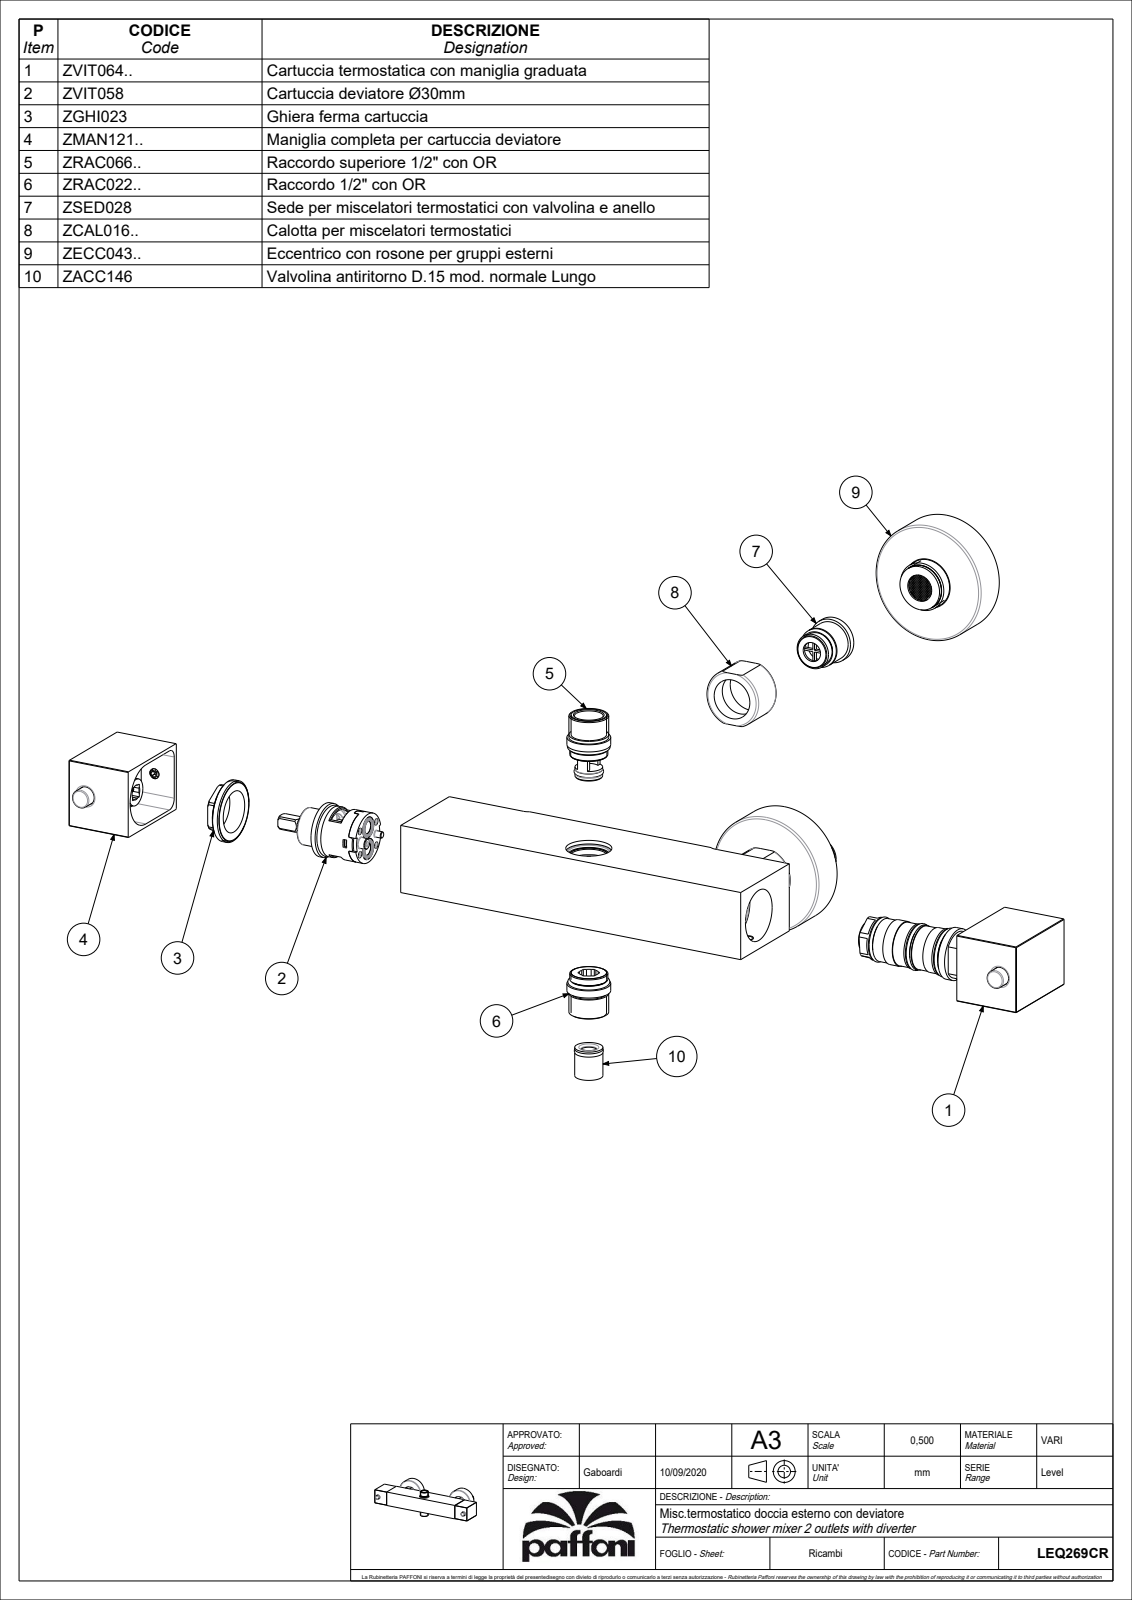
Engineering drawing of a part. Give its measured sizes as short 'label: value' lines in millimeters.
name: LEQ269CR
written by: CREO PARAMETRIC BY PTC INC, 2020044 (CONFIG_CONTROL_DESIGN)
unit: mm
bodies: 5 solids, 935 faces (349 planar, 352 cylindrical, 234 other)
size: 279.05 × 99.45 × 66.5
volume: 398 836 mm³; area: 160 190 mm²
holes: 4× ⌀6, 3× ⌀15.1, 2× ⌀2.5, 2× ⌀3, 2× ⌀3.25, 2× ⌀4, 2× ⌀4.5, 2× ⌀5.5, 2× ⌀6.4, 2× ⌀10.1, 2× ⌀10.5, 2× ⌀16
bosses: 2× ⌀63.5, 2× ⌀24, 2× ⌀21.2, 2× ⌀19, 2× ⌀14.5, 2× ⌀9.8, 2× ⌀7.6, 1× ⌀23
rounds: 84× R1, 16× R0.5, 6× R5, 2× R1.75, 2× R4.82, 2× R15.6, 1× R2.25, 1× R5.15
face distances: 37.5, 2.75, 34.75, 3.25, 3, 0.4, 48.75, 37.1, 2.35, 34.35
hole spacings: 6, 10, 15.28, 15.46, 4, 6.05, 6.25, 8
